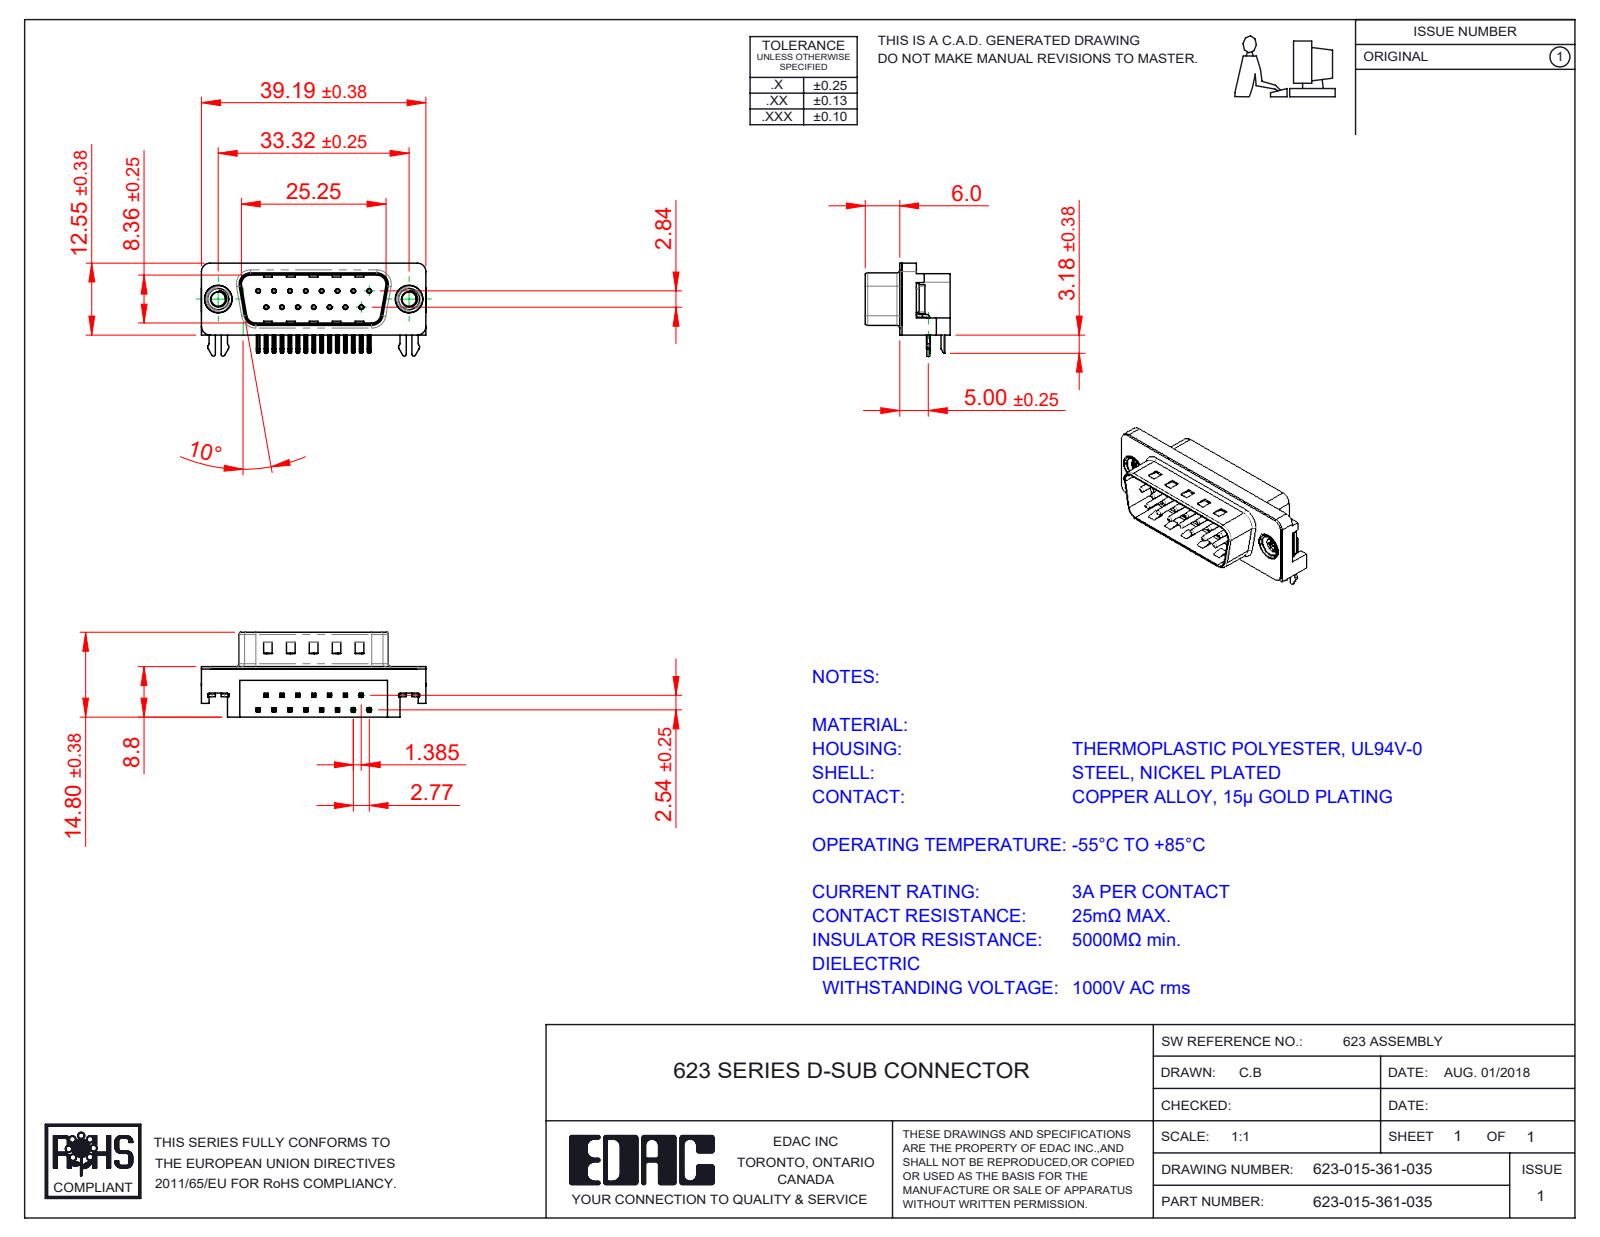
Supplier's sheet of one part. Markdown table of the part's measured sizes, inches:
| quantity | value |
| --- | --- |
| part name | 623 Housing_15 Socket; 623 Shell_15 Socket; 623 Contact Bottom; 623 Contact Top (+3 more) |
| STEP written by | SolidWorks 2016 (CONFIG_CONTROL_DESIGN) |
| units | inches |
| bodies | 21 solids, 1499 faces (921 planar, 443 cylindrical, 135 other) |
| overall size | 1.544 × 0.64 × 0.583 |
| volume | 0.203 in³ |
| surface area | 7.673 in² |
| round holes (diameter × count) | 0.014 × 15, 0.031 × 15, 0.098 × 2, 0.157 × 2, 0.189 × 2, 0.197 × 2 |
| round bosses / shafts (diameter × count) | 0.03 × 15, 0.193 × 2, 0.187 × 2, 0.154 × 2 |
| partial cylindrical surfaces (radius × count) | 0.01 × 68, 0.005 × 30, 0.02 × 14, 0.039 × 8, 0.059 × 6, 0.013 × 4, 0.035 × 4, 0.063 × 4 |
| main face-to-face distances | 0.016, 0.331, 0.083, 0.067, 0.412, 0.346, 0.428, 0.345, 0.232, 0.114 |
| hole center spacings | 0.124, 0.109, 0.218, 0.327, 0.436, 0.198, 0.198, 0.294 |
